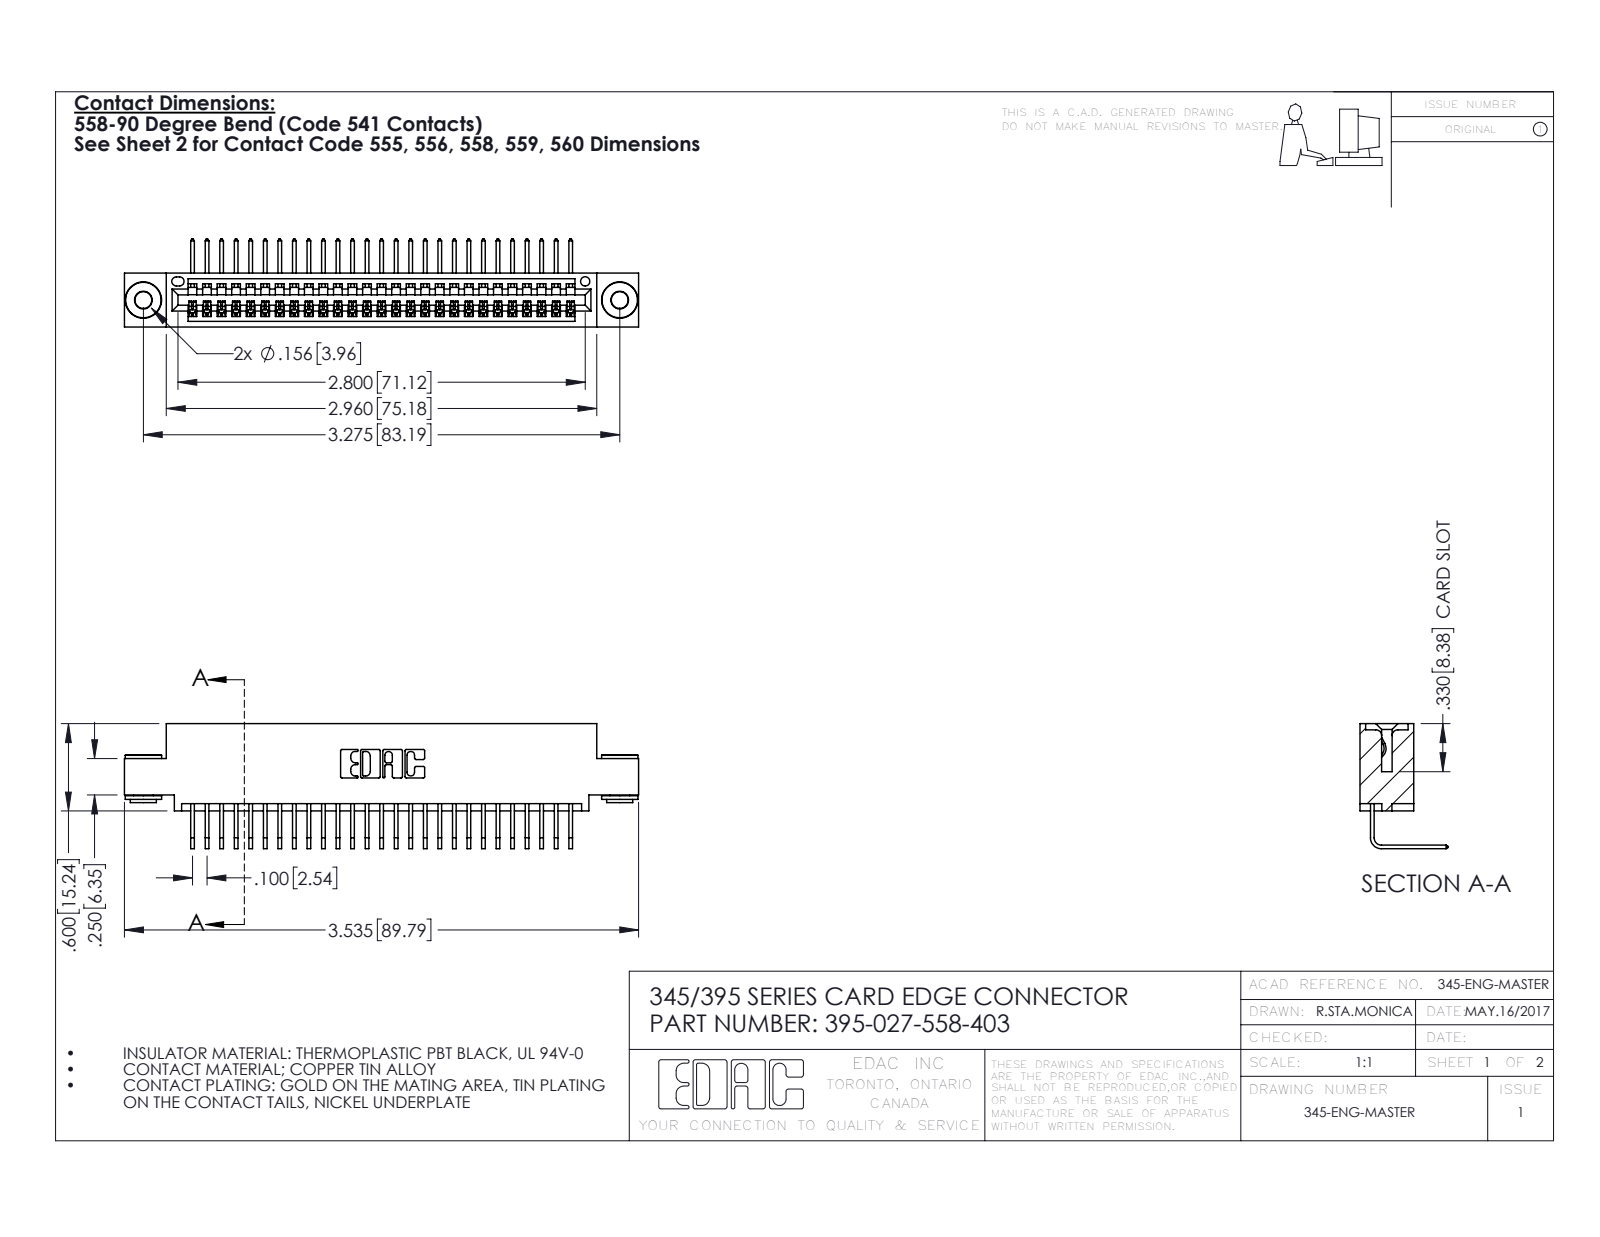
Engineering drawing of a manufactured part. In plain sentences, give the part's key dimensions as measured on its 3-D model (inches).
The part is named "345-250-002_345-250-002-102; 345-292-001_558 Tail - 2; 345 Part_0.110 Offset - 0.156 Dia-TH; 395-027-558-403". Its 3-D file was written by "SolidWorks 2016 (CONFIG_CONTROL_DESIGN)". It is 30 solids with 1788 faces: 1228 planar, 552 cylindrical and 8 other. Overall it measures 3.535 by 0.859 by 0.605 inches. Its volume is 0.515 cubic inches and its surface area 18.35 square inches. Round holes: 2 of diameter 0.116, 2 of diameter 0.156, 1 of diameter 0.064. Round bosses or shafts: 2 of diameter 0.25, 2 of diameter 0.18, 2 of diameter 0.136. Partial cylindrical surfaces (rounded edges, fillets, slot ends): 54 of radius 0.006, 22 of radius 0.01, 6 of radius 0.007, 6 of radius 0.031, 3 of radius 0.026, 2 of radius 0.031, 2 of radius 0.04, 1 of radius 0.014. The main face-to-face distances are 0.072, 0.298, 0.37, 0.2, 0.025, 0.098, 0.272, 0.225, 0.149, 0.072. The hole center spacings are 0.27, 3.04, 3.275.
